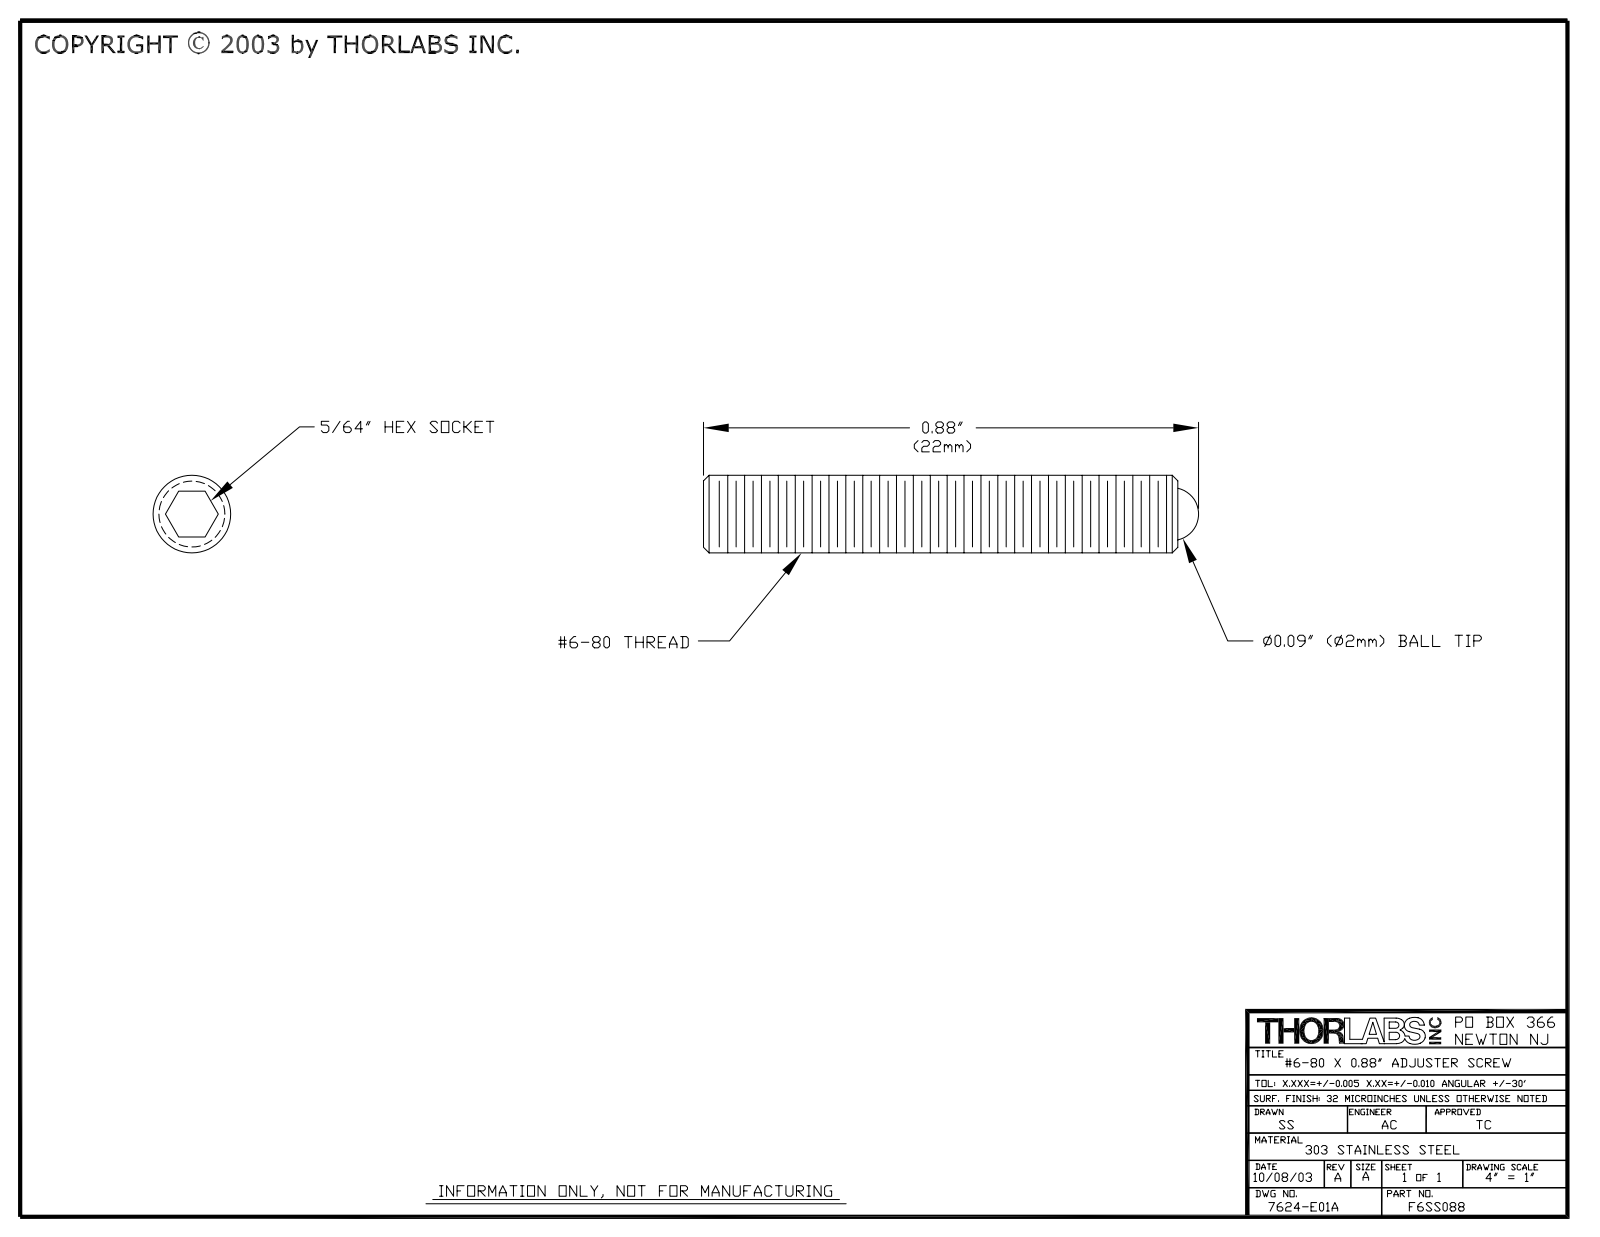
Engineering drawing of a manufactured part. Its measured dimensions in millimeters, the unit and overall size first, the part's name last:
Units: millimetres
Overall size (bounding box): 22.4 × 3.5 × 3.5
Round holes (diameter × count): ⌀2.4 ×1
Round bosses / shafts (diameter × count): ⌀3.5 ×1
Main face-to-face distances: 1.7, 21.4, 18.4, 3
Volume: 200 mm³ · Surface area: 294 mm²
Bodies: 2 solids, 23 faces (9 planar, 4 cylindrical, 10 other)
Part name (STEP PRODUCT): 7624-E0W
STEP written by: SolidWorks 2011 (AUTOMOTIVE_DESIGN)
